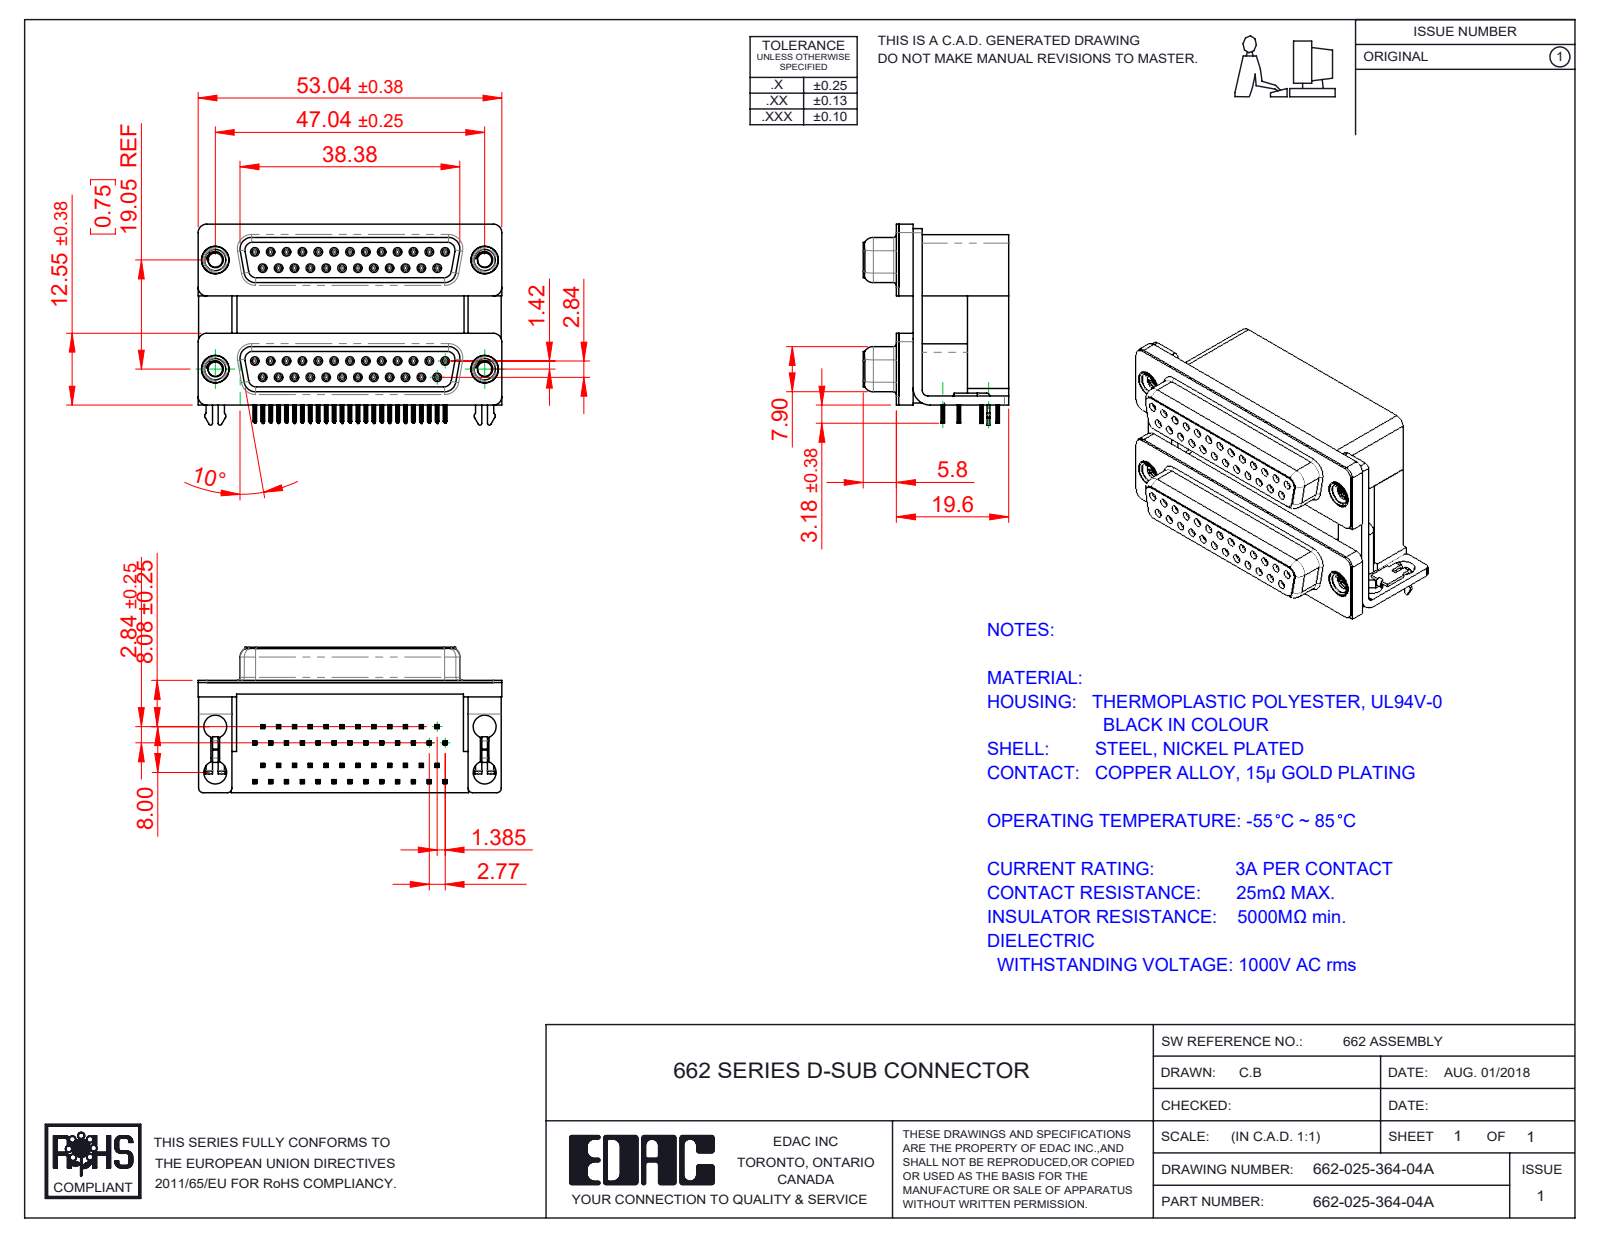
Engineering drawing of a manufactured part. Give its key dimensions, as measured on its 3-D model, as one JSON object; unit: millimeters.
{"part_name": "662 Contact Top Lower; 662 2 Prong Board Lock_4; 662 Threaded Rivet_M3; 662 Contact Top Upper_M (+8 more)", "step_written_by": "SolidWorks 2020 (CONFIG_CONTROL_DESIGN)", "units": "millimeters", "bodies": {"solids": 63, "faces": 7904, "planar": 3654, "cylindrical": 1842, "other": 2408}, "overall_size": [53.04, 35.1, 25.4], "volume_mm3": 23826, "surface_area_mm2": 26018, "round_holes": [[0.8, 50], [0.9, 50], [4, 8], [2.5, 4], [3.5, 4], [4.8, 4], [5, 4]], "round_bosses_or_shafts": [[1.2, 50], [4.9, 4], [4.75, 4], [3.9, 4]], "partial_cylinders_radius": [[0.1, 401], [0.15, 200], [0.35, 100], [0.34, 50], [0.28, 24], [1.35, 16], [1.5, 14], [0.5, 12]], "face_to_face_distances": [19.2, 19.05, 12, 0.4, 7.2, 6.2, 10.69, 2.5, 16.7, 9.5], "hole_center_spacings": [3.16, 2.77, 5.54, 11.08, 8.31, 5.03, 13.85, 7.48]}
